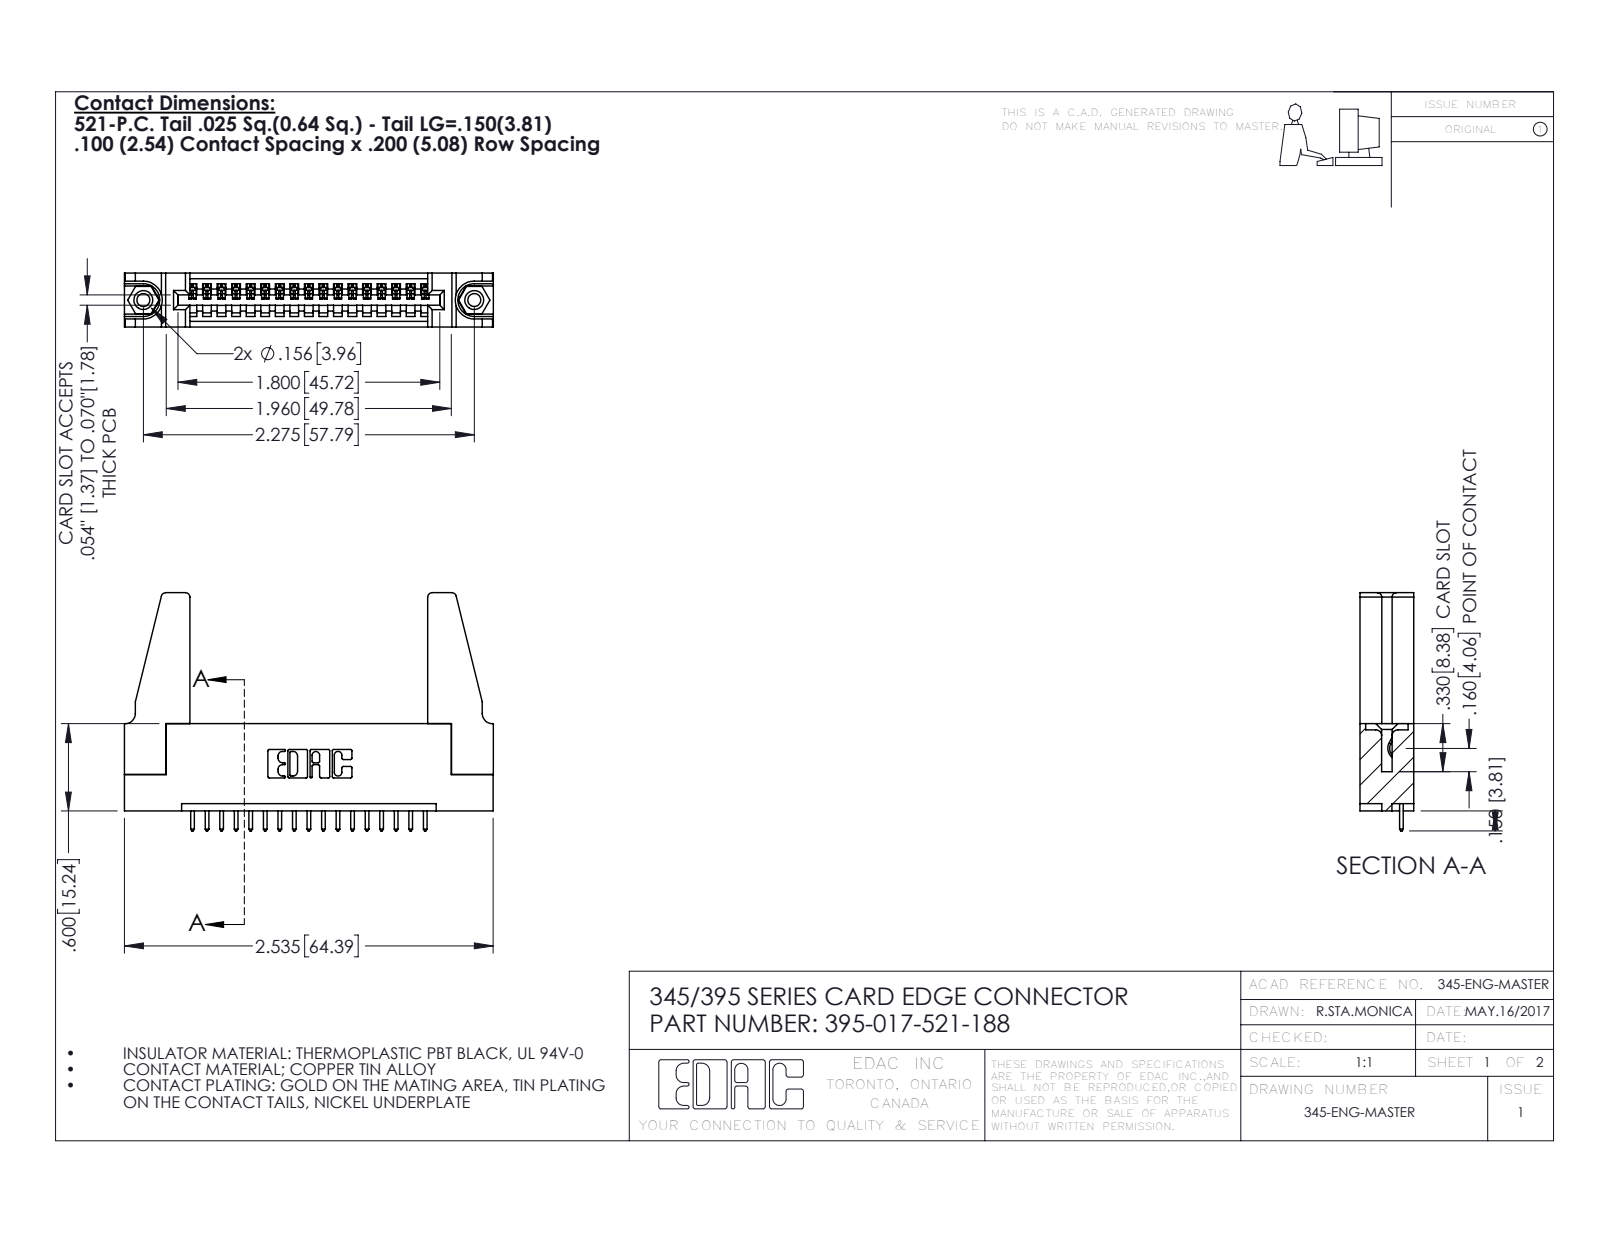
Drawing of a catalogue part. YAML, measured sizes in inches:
part_name: "345-292-001_345-293-121; 395-017-521-188; 345-250-001_345-250-001-102; 345 Part_Flush Mounting Lugs - 0.156 Dia-TH (+1 more)"
step_written_by: "SolidWorks 2016 (CONFIG_CONTROL_DESIGN)"
units: inches
bodies: {solids: 22, faces: 1236, planar: 832, cylindrical: 388, other: 16}
overall_size: [2.536, 1.637, 0.37]
volume: 0.556
surface_area: 16.11
round_holes:
  - {diameter: 0.089, count: 2}
  - {diameter: 0.125, count: 2}
  - {diameter: 0.156, count: 2}
  - {diameter: 0.064, count: 1}
round_bosses_or_shafts:
  - {diameter: 0.155, count: 2}
partial_cylinders:
  - {radius: 0.006, count: 34}
  - {radius: 0.01, count: 34}
  - {radius: 0.01, count: 22}
  - {radius: 0.03, count: 8}
  - {radius: 0.007, count: 6}
  - {radius: 0.031, count: 6}
  - {radius: 0.026, count: 3}
  - {radius: 0.031, count: 2}
face_to_face_distances: [0.37, 0.072, 0.298, 0.2, 0.098, 0.272, 0.025, 0.225, 0.15, 0.148]
hole_center_spacings: [0.27, 2.041, 2.275]
